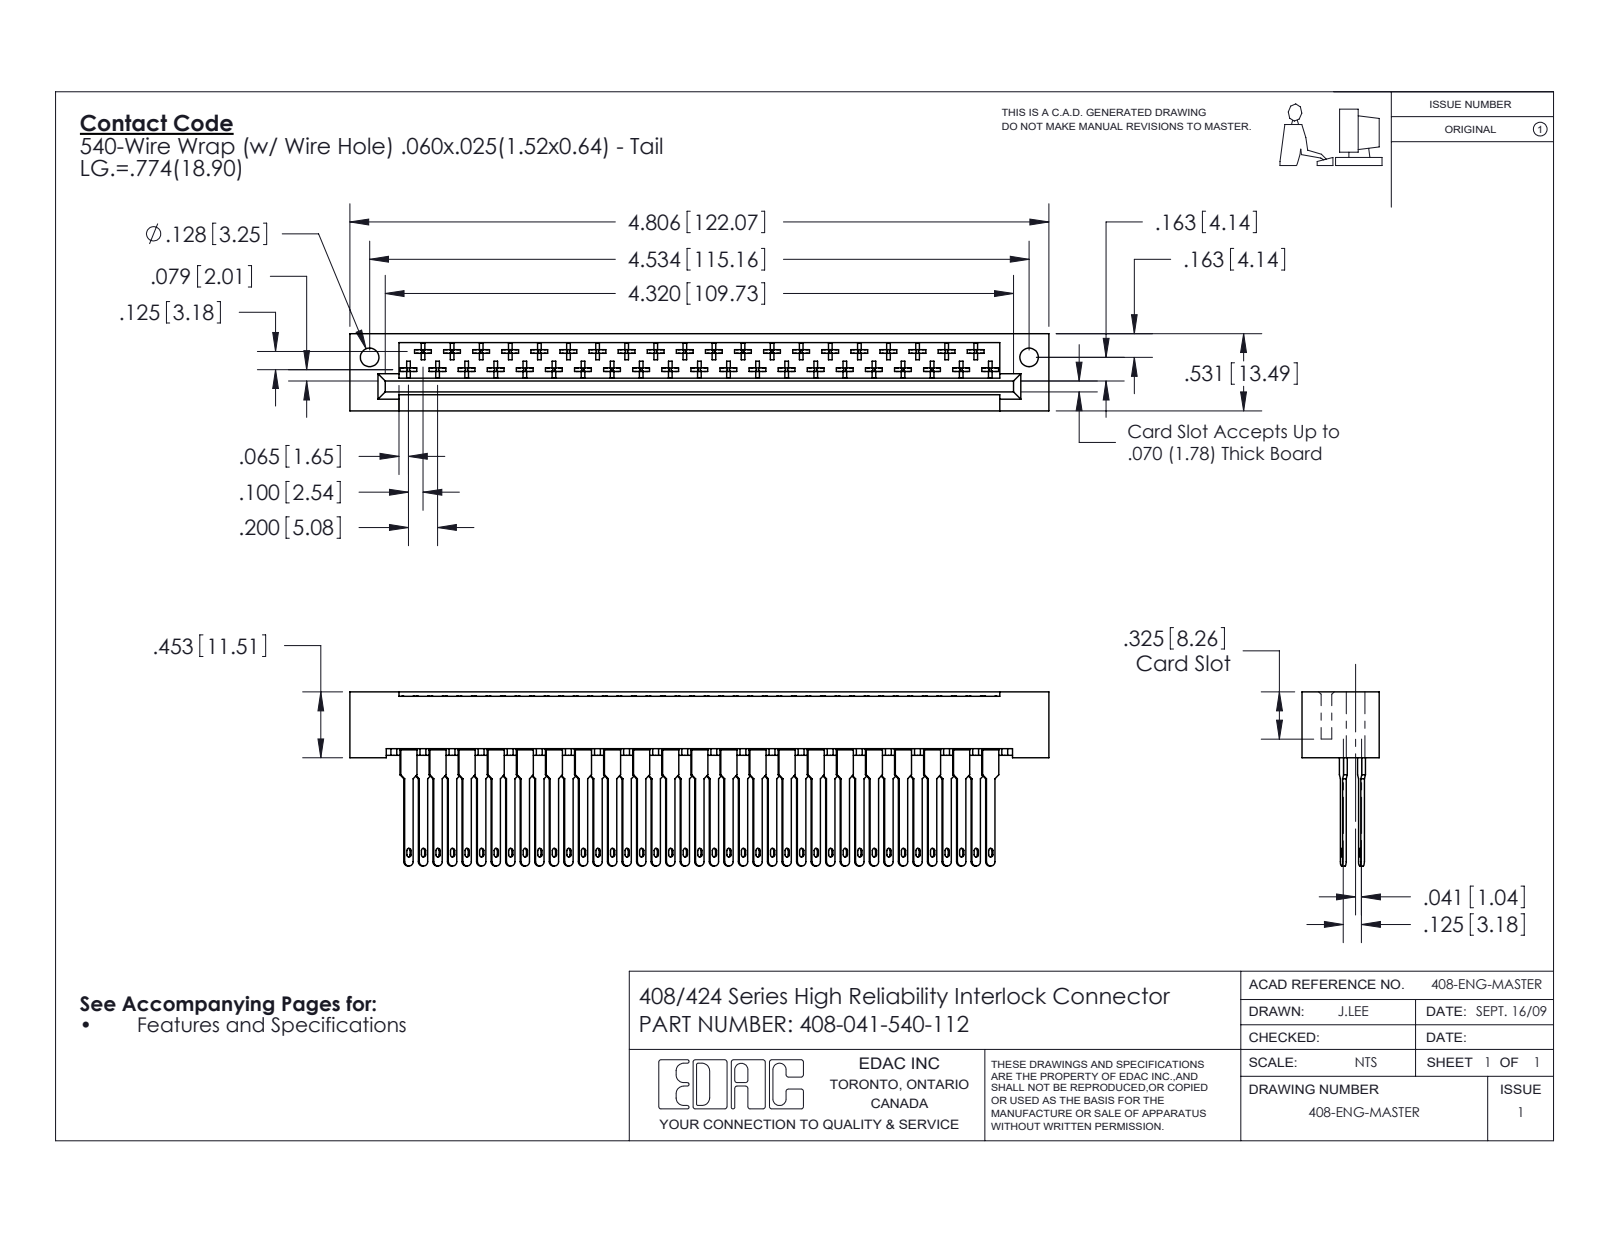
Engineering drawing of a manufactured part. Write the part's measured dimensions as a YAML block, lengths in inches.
part_name: "408 Part_041 - 1; 408-290-001_408-290-140; 408-041-540-112"
step_written_by: "SolidWorks 2016 (CONFIG_CONTROL_DESIGN)"
units: inches
bodies: {solids: 42, faces: 2381, planar: 1758, cylindrical: 459, other: 164}
overall_size: [4.806, 1.197, 0.531]
volume: 0.895
surface_area: 30.66
round_holes:
  - {diameter: 0.128, count: 2}
partial_cylinders:
  - {radius: 0.01, count: 246}
  - {radius: 0.015, count: 82}
  - {radius: 0.02, count: 43}
  - {radius: 0.03, count: 41}
face_to_face_distances: [0.531, 0.1, 0.125, 0.025, 0.025, 0.4, 0.259, 0.272, 0.235, 0.296]
hole_center_spacings: [4.534]
